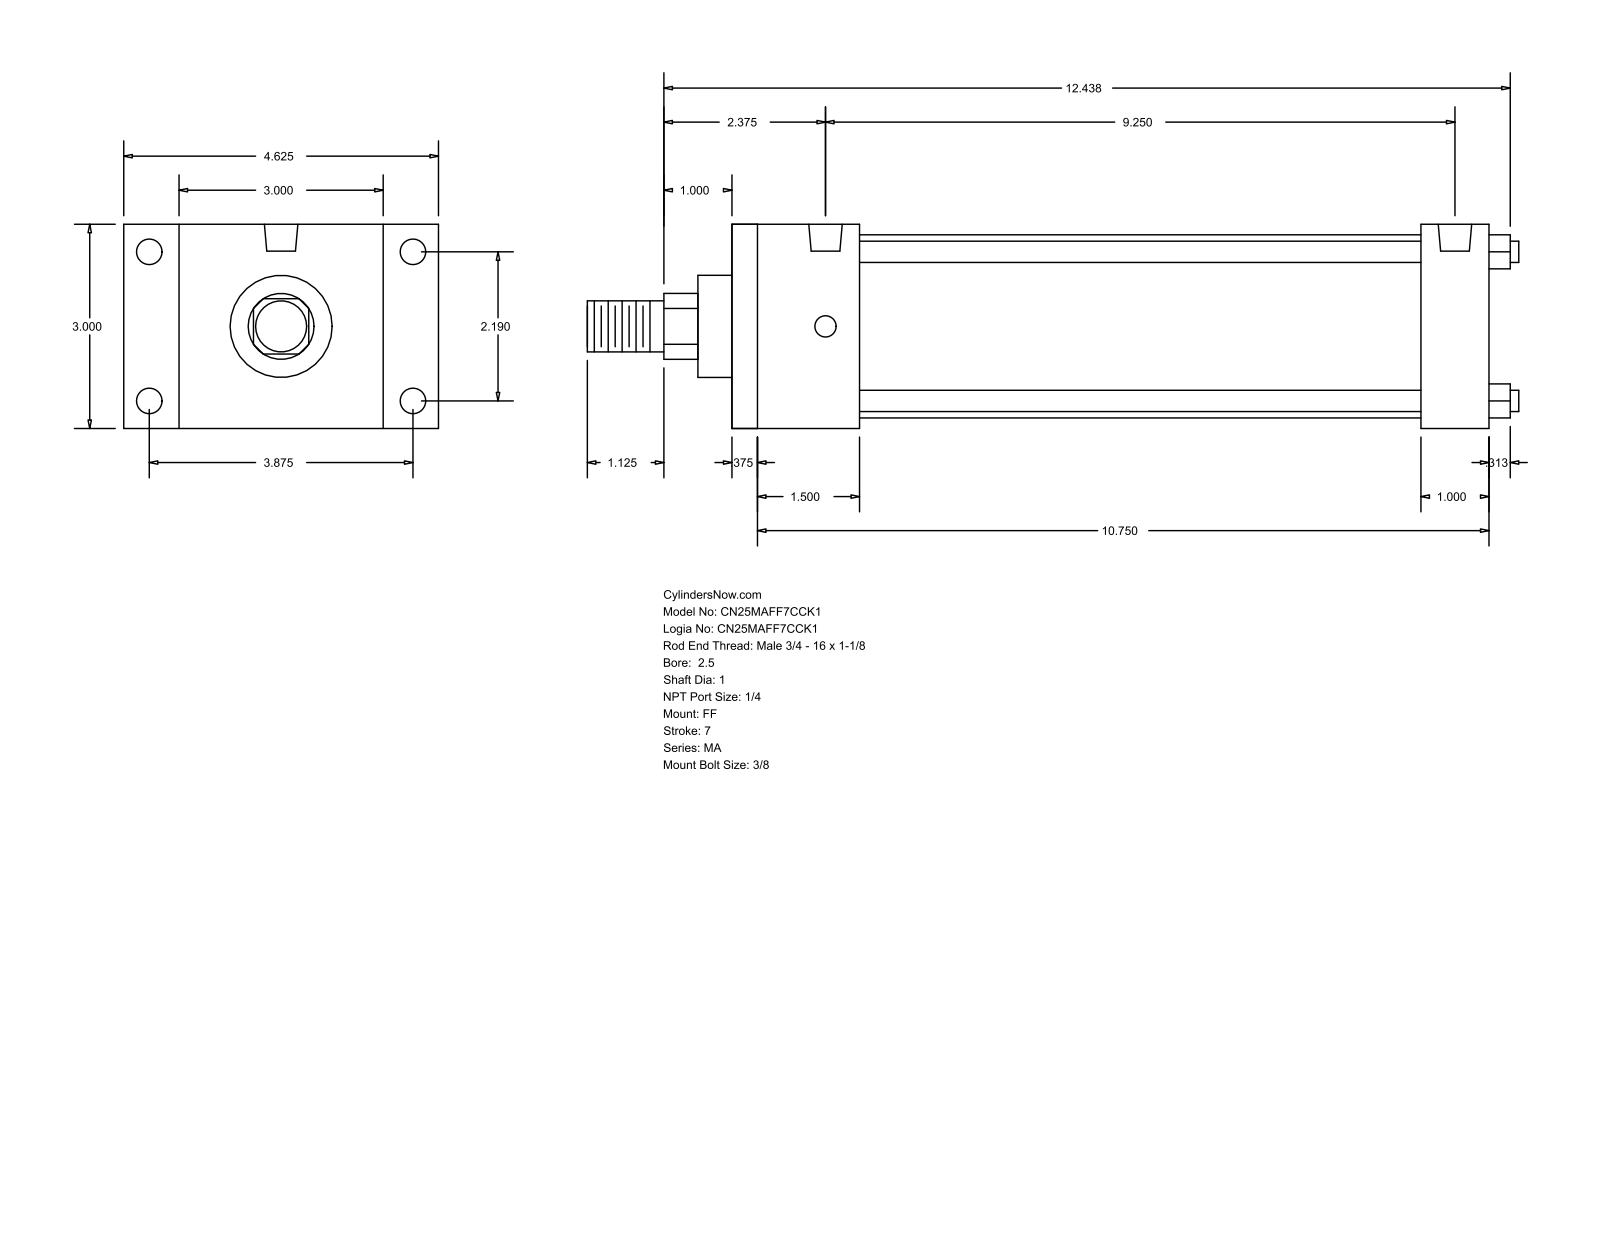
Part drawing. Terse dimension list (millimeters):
name: MA_FF__0250_1
written by: GSSL Pune (CONFIG_CONTROL_DESIGN)
unit: mm
bodies: 0 solids, 92 faces (64 planar, 28 cylindrical, 0 other)
size: 347.66 × 117.47 × 76.2
holes: 4× ⌀7.94, 4× ⌀9.53, 2× ⌀12.49
bosses: 4× ⌀7.94, 1× ⌀68.33, 1× ⌀38.1, 1× ⌀25.4, 1× ⌀19.05
rounds: 1× R12.29
face distances: 76.2, 282.58, 9.52, 273.06, 47.63, 257.17, 38.11, 247.65, 209.54, 234.95
hole spacings: 55.62, 98.42, 113.05, 234.94
